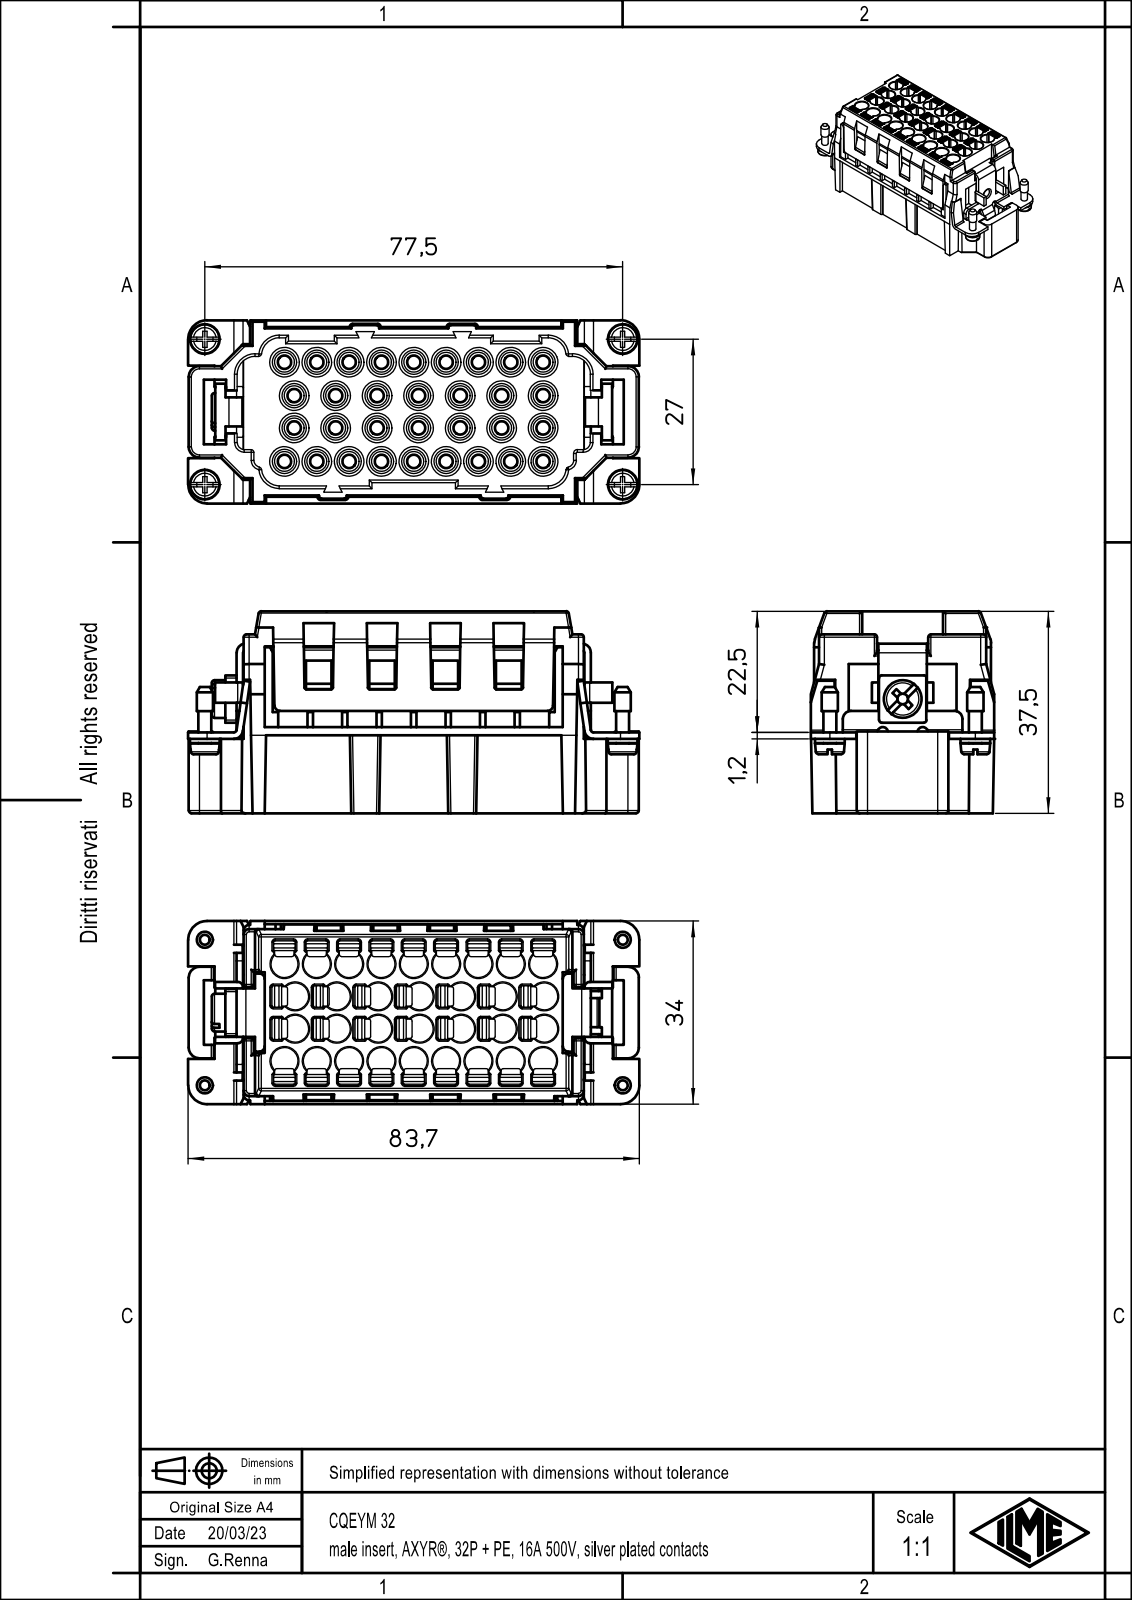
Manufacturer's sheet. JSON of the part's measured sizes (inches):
{"part_name": "CQEYM 32", "step_written_by": "Creo Elements/Direct Modeling 20.1B 02-Apr-2019 (C) Parametric Technology GmbH (AUTOMOTIVE_DESIGN)", "units": "inches", "bodies": {"solids": 1, "faces": 3234, "planar": 1490, "cylindrical": 1196, "other": 548}, "overall_size": [3.295, 1.476, 1.339], "volume_in3": 3.128, "surface_area_in2": 55.63, "round_holes": [[0.079, 1], [0.13, 1]], "round_bosses_or_shafts": [[0.177, 32], [0.098, 32], [0.217, 4], [0.118, 4], [0.094, 4], [0.276, 1], [0.224, 1], [0.157, 1]], "partial_cylinders_radius": [[0.008, 160], [0.016, 128], [0.02, 89], [0.012, 80], [0.004, 64], [0.098, 34], [0.039, 24], [0.079, 17]], "face_to_face_distances": [0.047, 0.051, 0.033, 0.071, 1.193, 1.24, 0.104, 0.024, 0.067, 0.026]}
